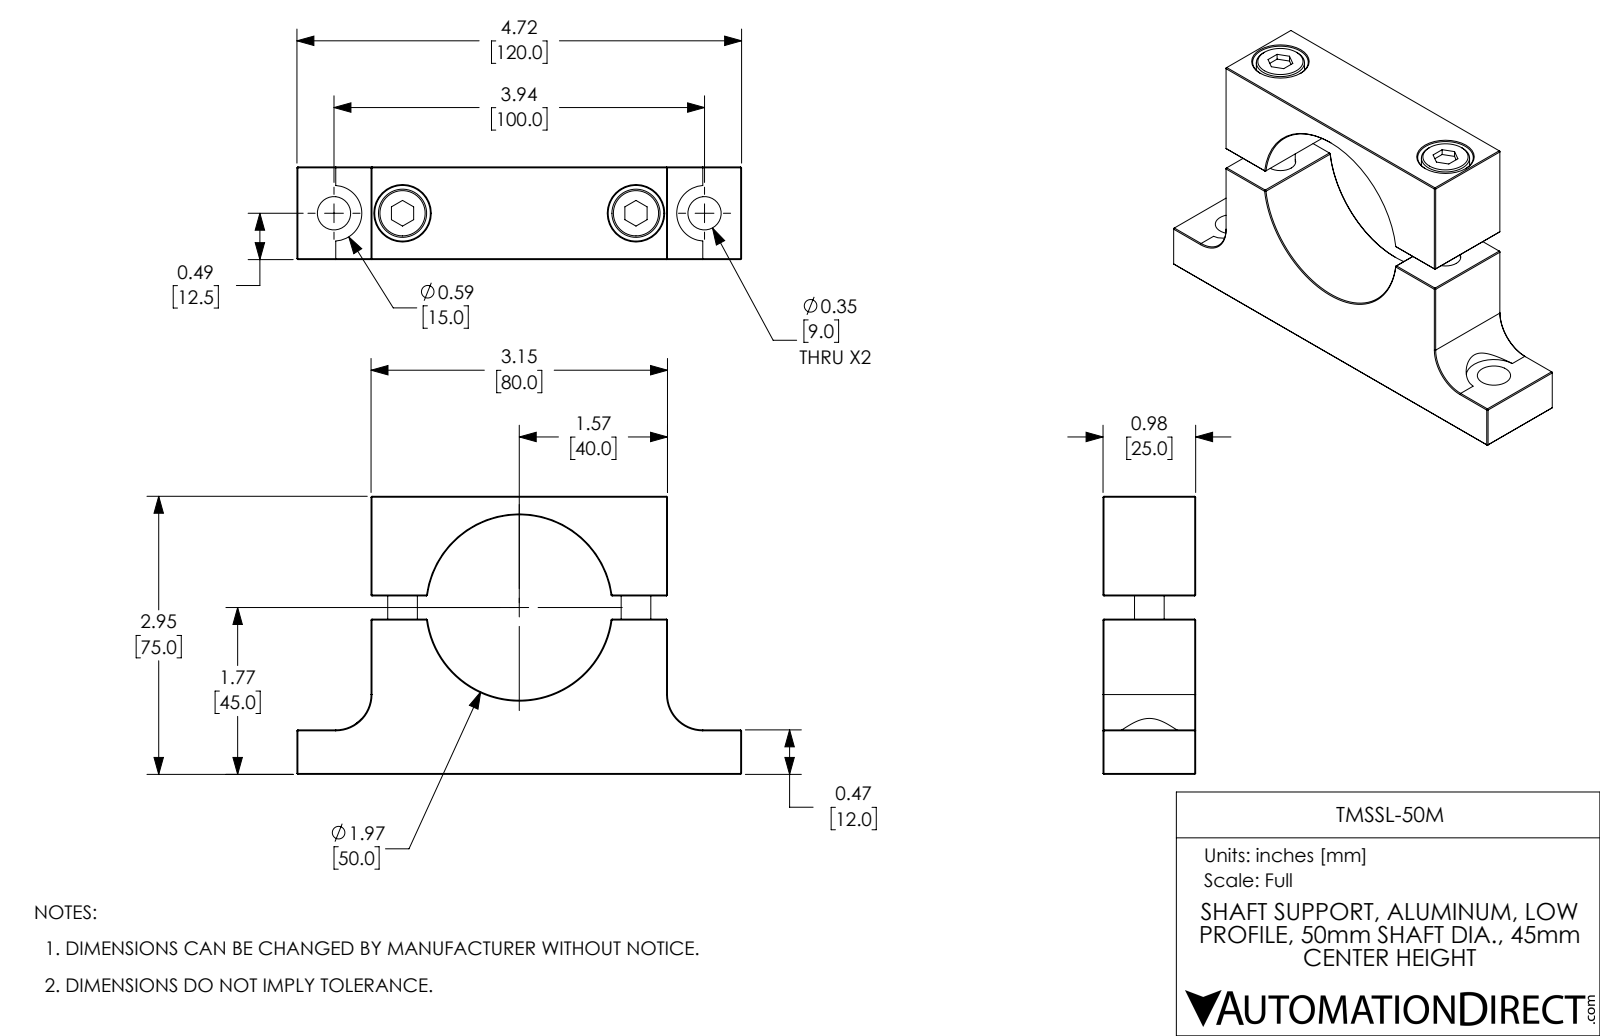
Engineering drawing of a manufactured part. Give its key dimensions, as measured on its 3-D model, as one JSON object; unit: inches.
{"part_name": "TMSSL-50M", "step_written_by": "SolidWorks 2017 (AUTOMOTIVE_DESIGN)", "units": "inches", "bodies": {"solids": 4, "faces": 169, "planar": 110, "cylindrical": 31, "other": 28}, "overall_size": [4.724, 2.953, 0.984], "volume_in3": 6.43, "surface_area_in2": 46.05, "round_holes": [[0.354, 4], [0.262, 2], [0.591, 2], [1.969, 1]], "round_bosses_or_shafts": [[0.512, 2], [0.315, 2]], "partial_cylinders_radius": [[0.296, 2], [0.375, 2]], "face_to_face_distances": [0.984, 2.953, 3.15, 1.894, 1.058, 0.787, 3.937, 2.48, 0.472, 1.422], "hole_center_spacings": [0.728, 3.209, 2.48, 3.937]}
